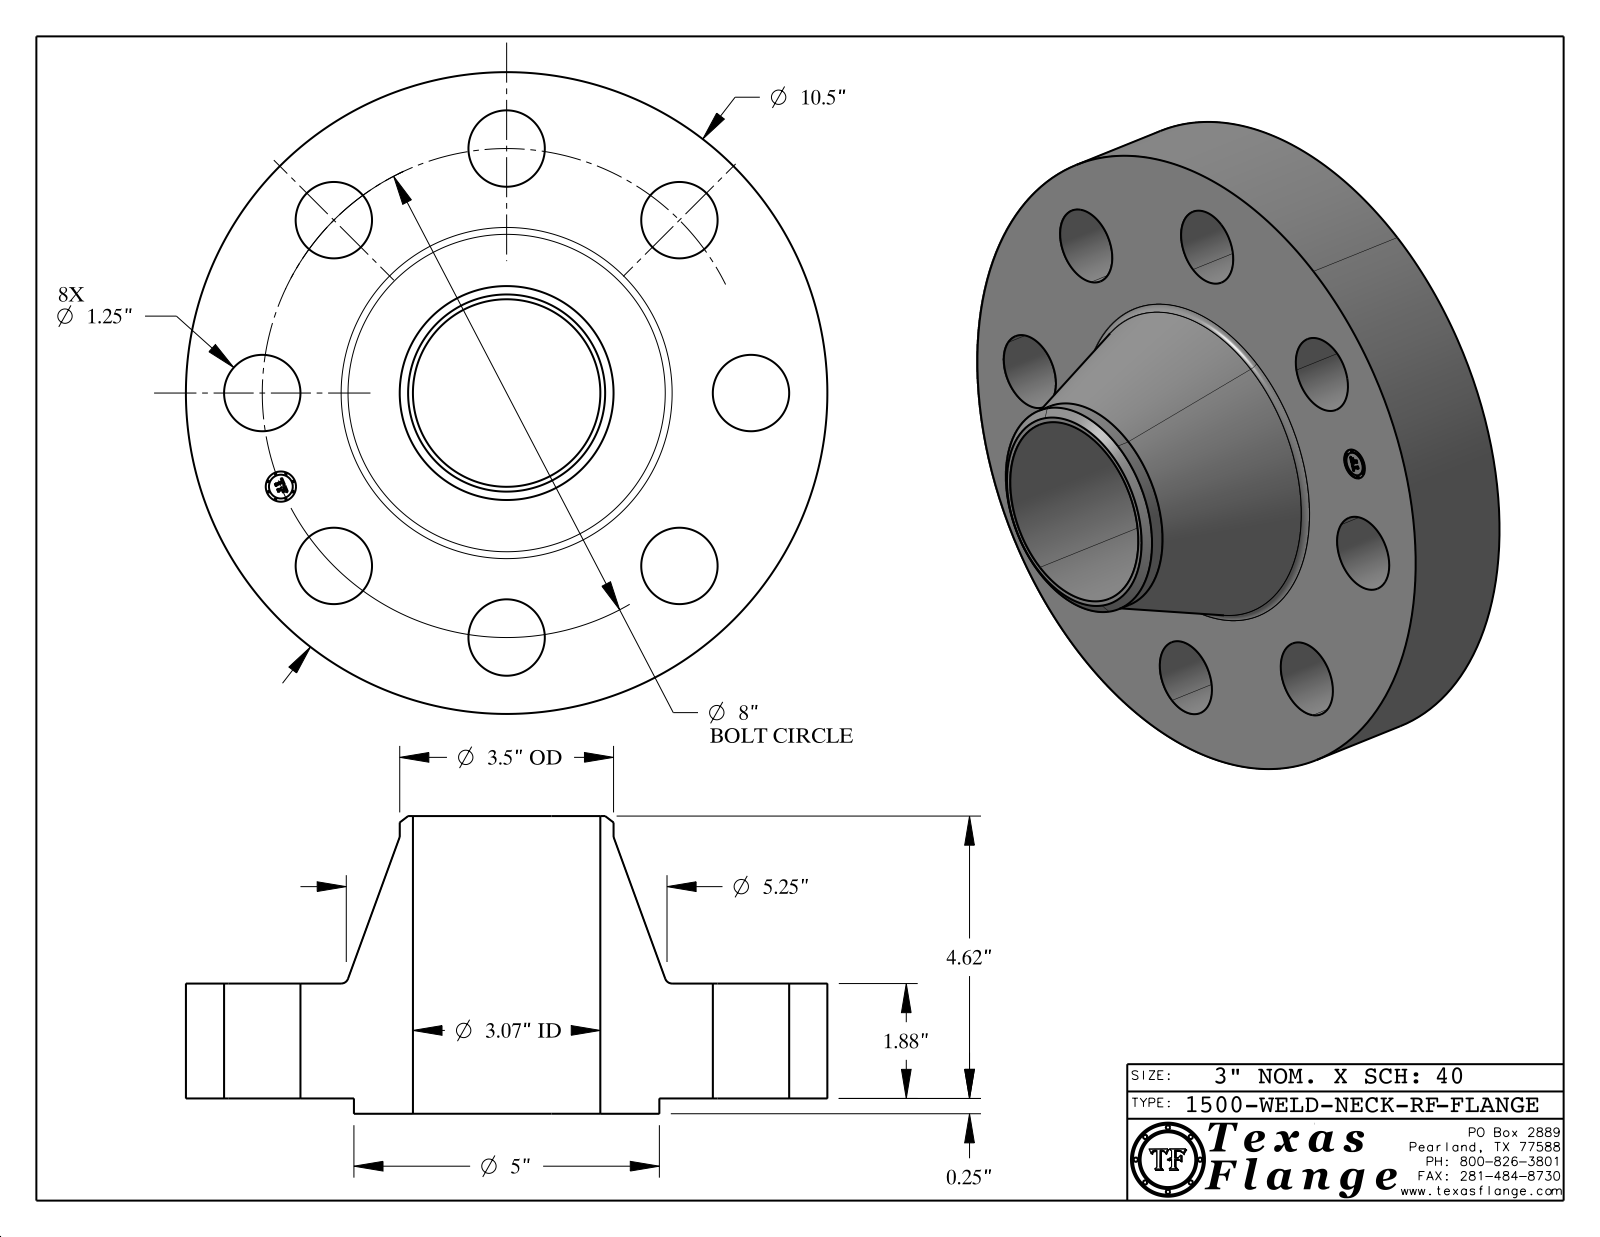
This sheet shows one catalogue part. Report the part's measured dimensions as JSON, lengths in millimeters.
{"part_name": "1500-WELD-NECK-RF", "step_written_by": "CATIA V5 STEP AP214 (AUTOMOTIVE_DESIGN)", "units": "millimeters", "bodies": {"solids": 1, "faces": 419, "planar": 369, "cylindrical": 44, "other": 6}, "overall_size": [266.7, 266.7, 123.7], "volume_mm3": 2507000, "surface_area_mm2": 217100, "round_holes": [[31.8, 8], [12.6, 1], [77.9, 1]], "round_bosses_or_shafts": [[0.8, 8], [266.7, 1], [127, 1], [88.9, 1], [9.9, 1]], "face_to_face_distances": [47.8, 6.4, 54.1, 123.7, 117.3, 69.6, 0.4, 53.7, 47.4, 70], "hole_center_spacings": [101.6, 77.7, 143.7, 187.7, 39.6, 169, 199.3, 203.2]}
